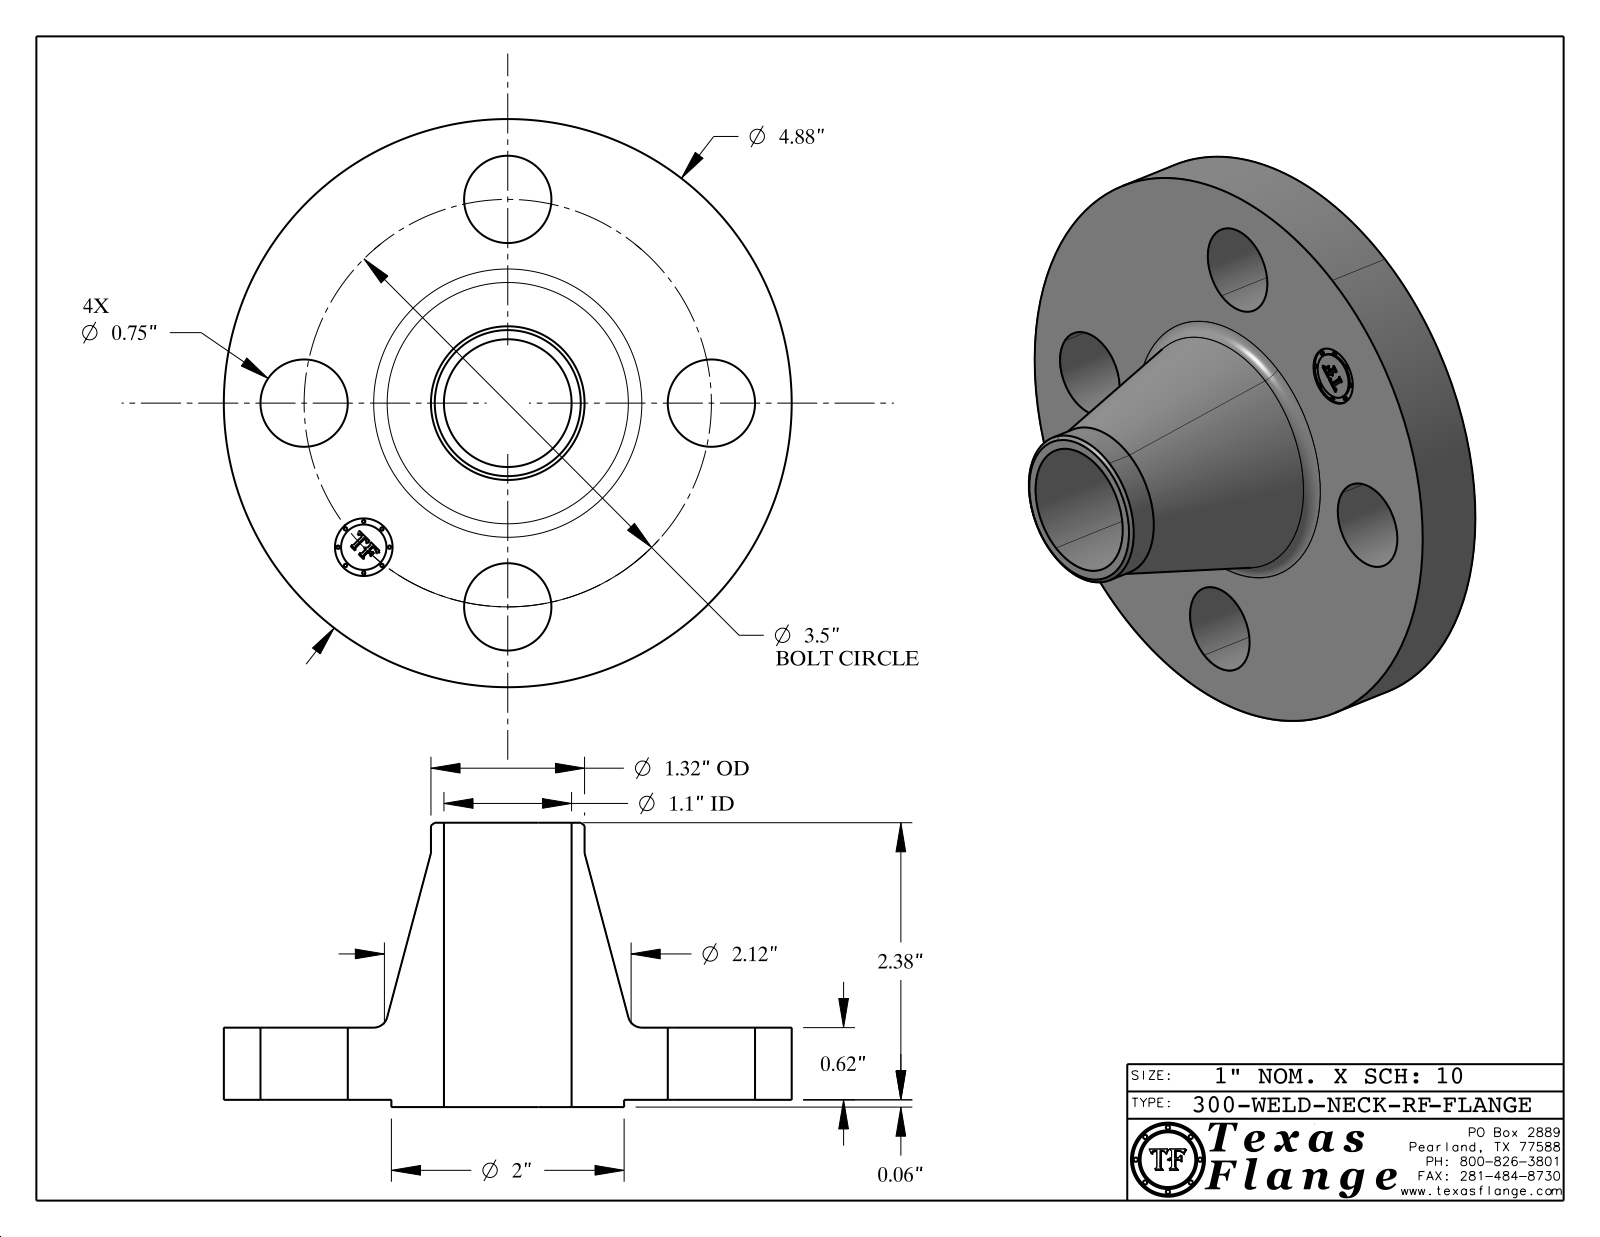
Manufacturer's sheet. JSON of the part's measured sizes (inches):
{"part_name": "300-WELD-NECK-RF", "step_written_by": "CATIA V5 STEP AP214 (AUTOMOTIVE_DESIGN)", "units": "inches", "bodies": {"solids": 1, "faces": 411, "planar": 369, "cylindrical": 36, "other": 6}, "overall_size": [4.88, 4.88, 2.443], "volume_in3": 12.3, "surface_area_in2": 63.29, "round_holes": [[0.75, 4], [0.495, 1], [1.097, 1]], "round_bosses_or_shafts": [[0.03, 8], [4.88, 1], [2, 1], [1.32, 1], [0.39, 1]], "face_to_face_distances": [0.62, 0.063, 0.683, 2.443, 2.38, 1.76, 0.015, 0.668, 0.605, 1.775], "hole_center_spacings": [1.75, 2.475, 1.339, 3.233, 3.5]}
